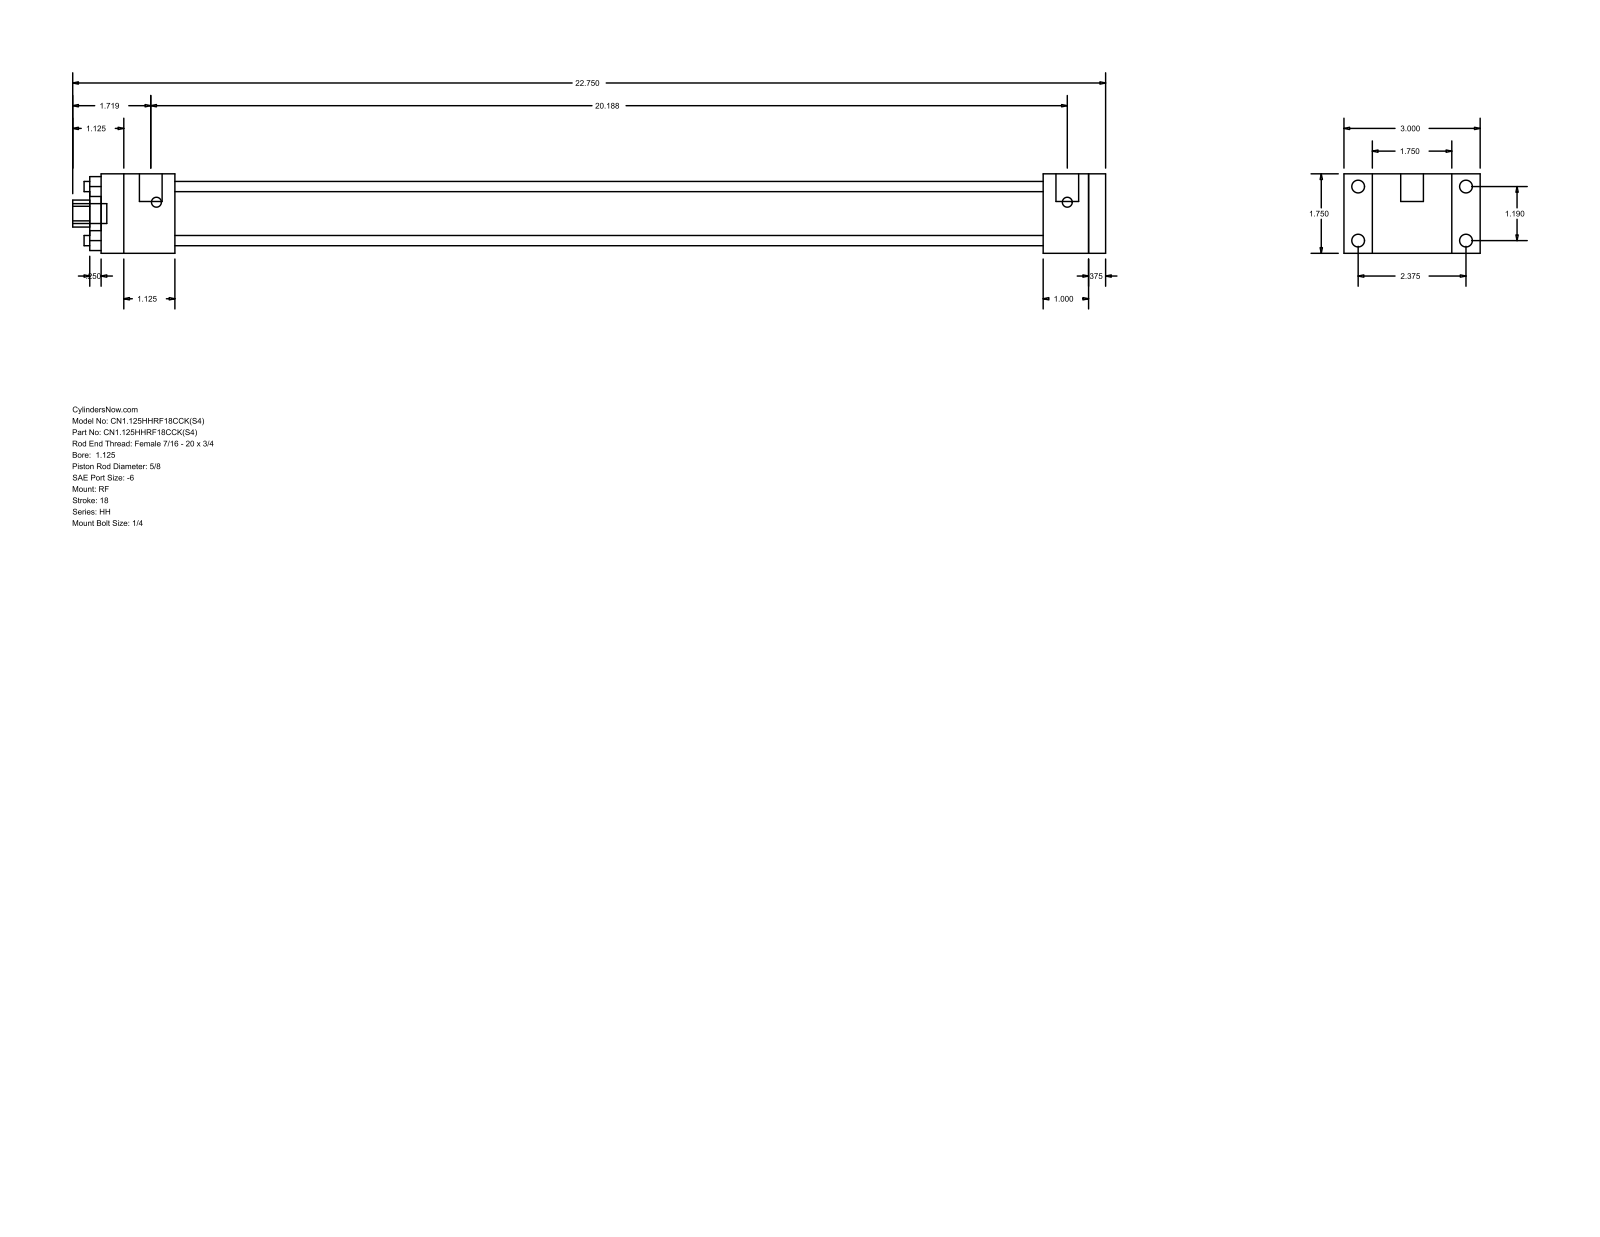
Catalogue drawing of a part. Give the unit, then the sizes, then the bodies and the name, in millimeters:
Units: millimetres
Overall size (bounding box): 577.85 × 76.2 × 44.45
Round holes (diameter × count): ⌀5.71 ×4, ⌀15.88 ×1, ⌀28.57 ×1, ⌀34.92 ×1
Round bosses / shafts (diameter × count): ⌀7.14 ×4, ⌀5.56 ×4, ⌀12.7 ×2, ⌀11.11 ×1
Partial cylindrical surfaces — rounded edges, fillets, slot ends (radius × count): R7.54 ×1
Main face-to-face distances: 44.46, 9.52, 15.87, 511.18, 520.7, 485.77, 25.41, 34.93, 41.27, 527.04
Hole centre spacings: 21.37, 30.22, 42.74
Bodies: 0 solids, 92 faces (64 planar, 28 cylindrical, 0 other)
Part name (STEP PRODUCT): HH_RF__0112_0.625
STEP written by: GSSL Pune (CONFIG_CONTROL_DESIGN)
